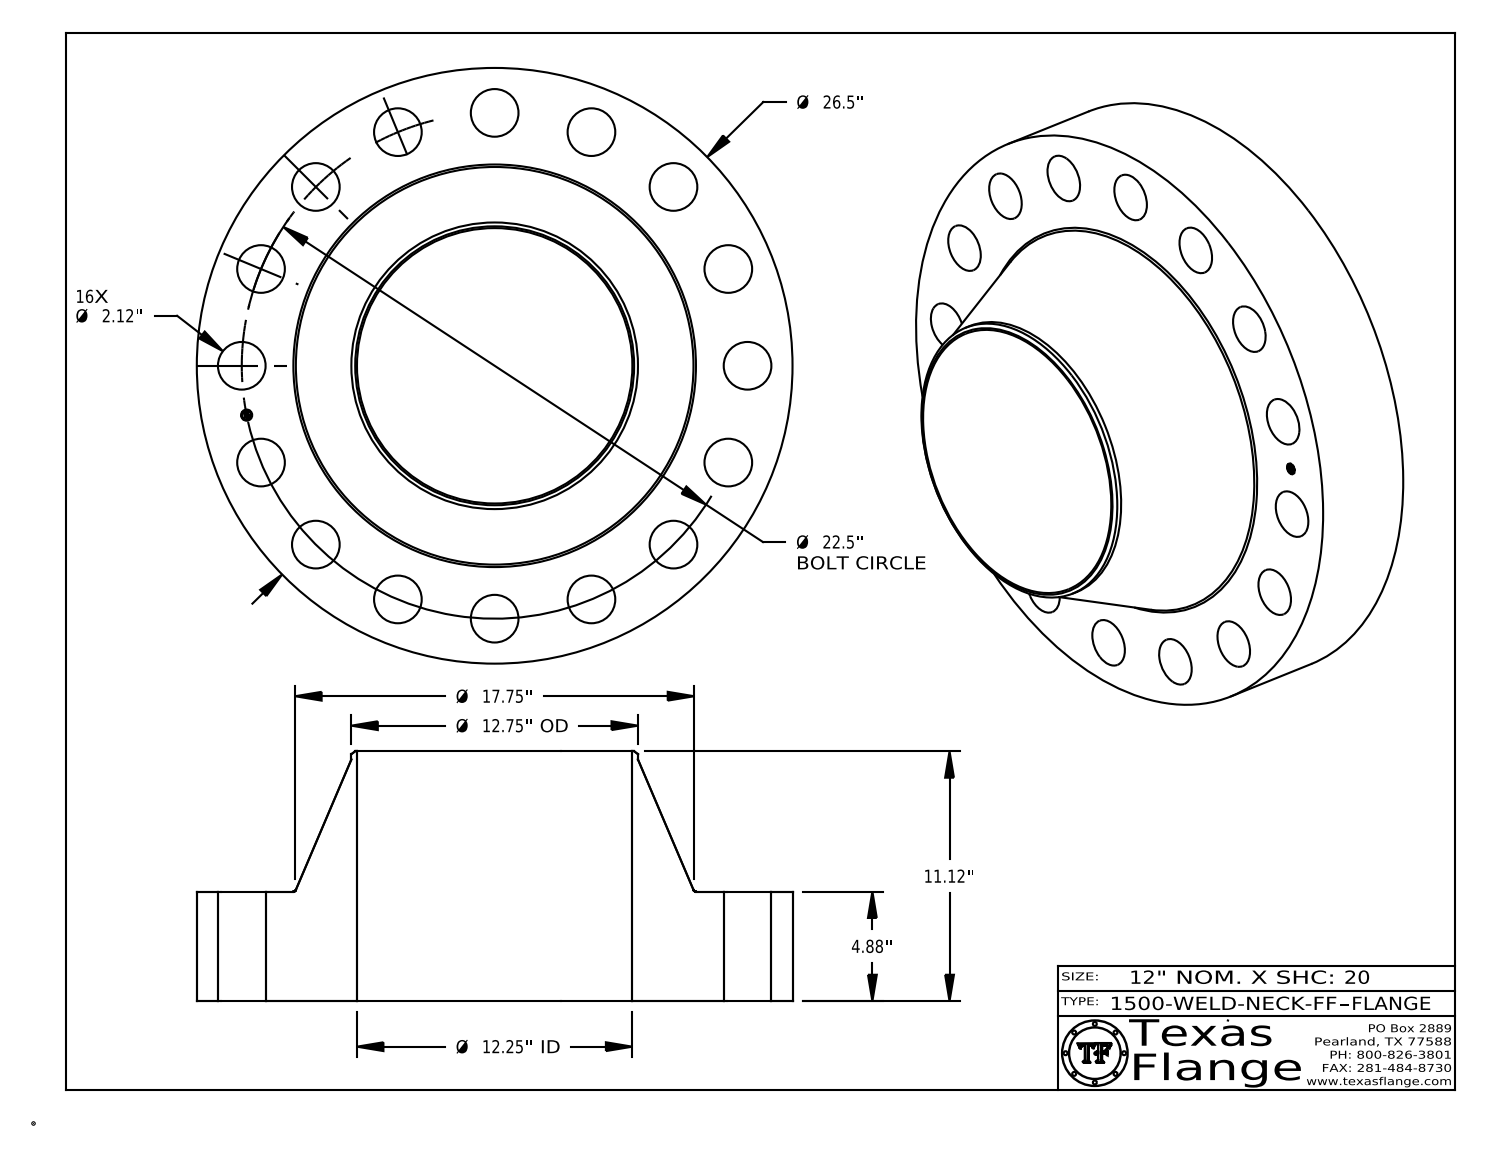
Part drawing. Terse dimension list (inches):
name: 1500-WELD-NECK-FF
written by: CATIA V5 STEP AP214 (AUTOMOTIVE_DESIGN)
unit: in
bodies: 1 solid, 432 faces (368 planar, 58 cylindrical, 6 other)
size: 26.5 × 26.5 × 11.12
volume: 2 234 in³; area: 2 305 in²
holes: 16× ⌀2.12, 1× ⌀0.495, 1× ⌀12.25
bosses: 8× ⌀0.03, 1× ⌀26.5, 1× ⌀12.75, 1× ⌀0.39
face distances: 4.88, 11.12, 6.24, 4.865, 0.015, 6.255, 0.148, 0.145, 0.027, 0.096
hole spacings: 12.5, 20.787, 22.068, 11.25, 8.611, 15.91, 4.389, 4.39
